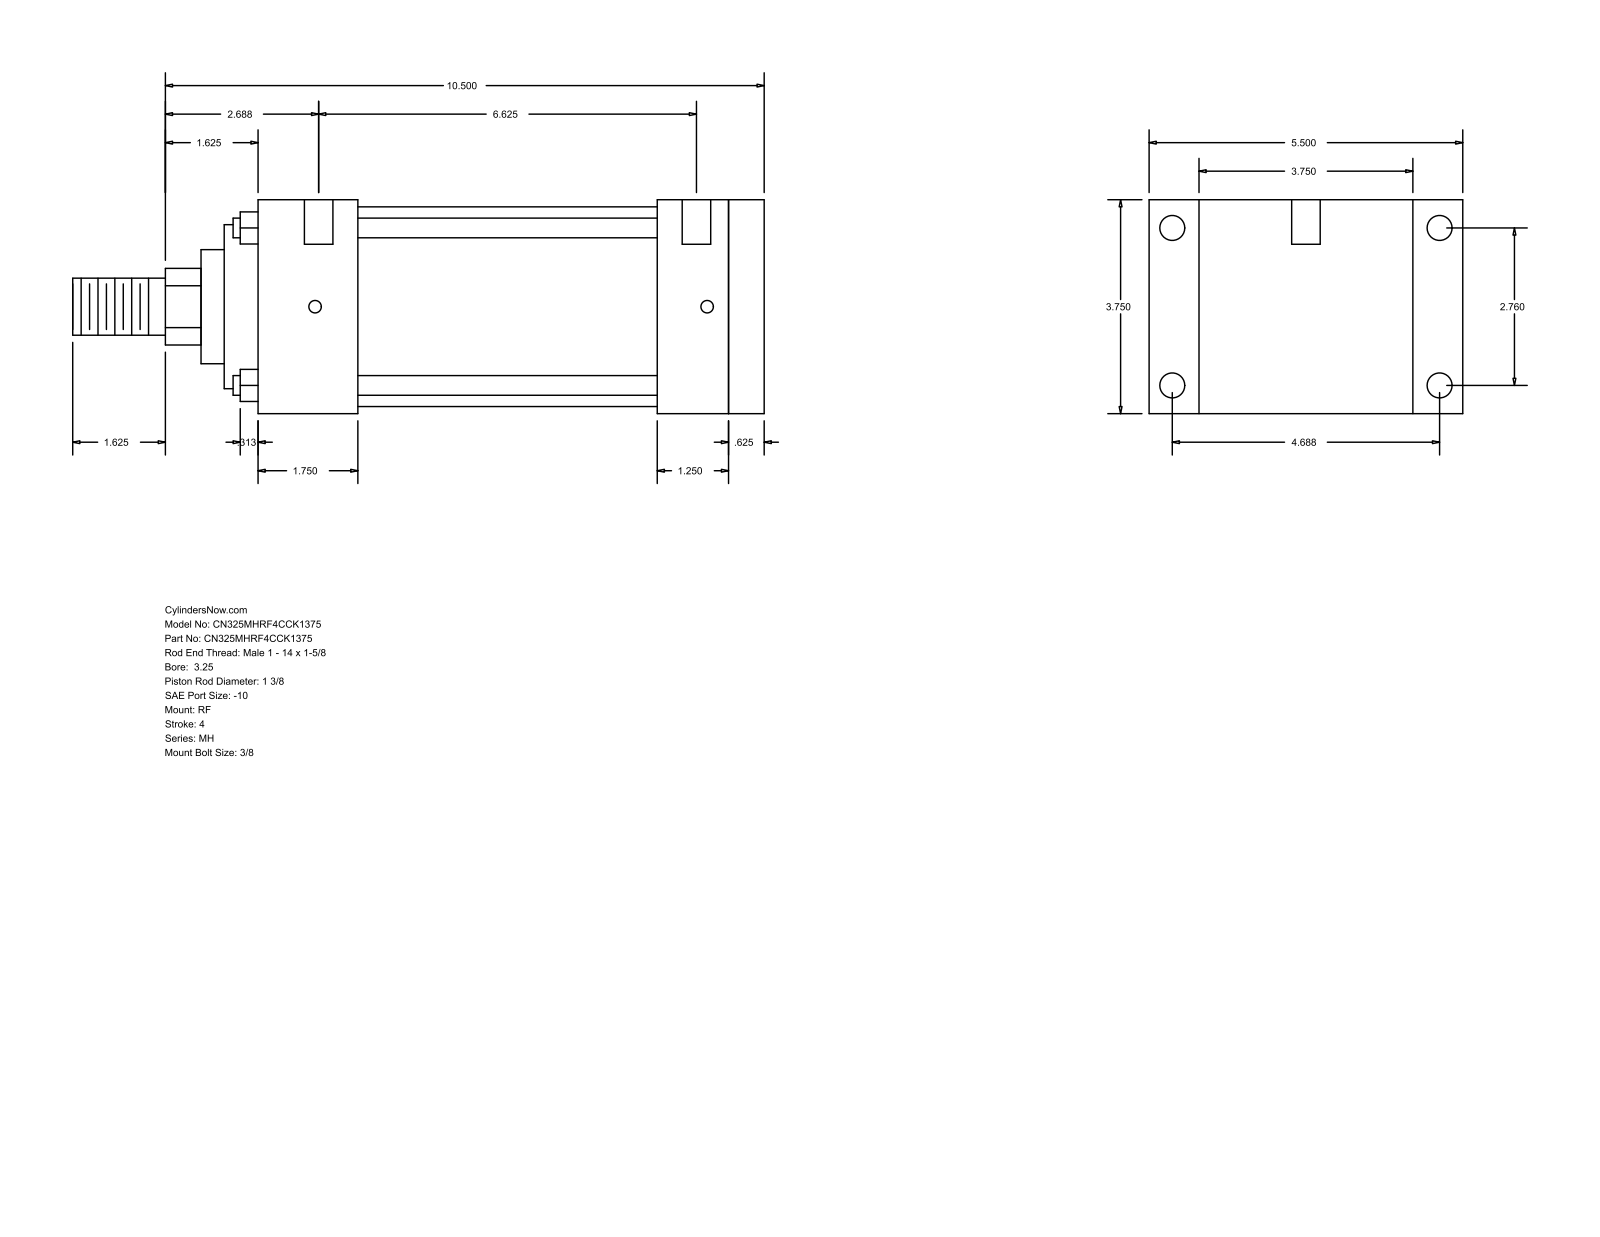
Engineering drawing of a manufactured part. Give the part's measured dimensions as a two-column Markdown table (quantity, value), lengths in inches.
| quantity | value |
| --- | --- |
| part name | MH_RF__0325_1.375 |
| STEP written by | GSSL Pune (CONFIG_CONTROL_DESIGN) |
| units | inches |
| bodies | 0 solids, 94 faces (65 planar, 29 cylindrical, 0 other) |
| overall size | 12.125 × 5.5 × 3.75 |
| round holes (diameter × count) | 0.219 × 4, 0.438 × 4, 0.5 × 2 |
| round bosses / shafts (diameter × count) | 0.345 × 4, 3.5 × 1, 2.875 × 1, 2 × 1, 1.375 × 1, 1 × 1 |
| partial cylindrical surfaces (radius × count) | 0.672 × 1 |
| main face-to-face distances | 3.75, 8.875, 0.625, 8.25, 0.875, 4.625, 1.75, 6.5, 7.125, 7 |
| hole center spacings | 2.76, 4.687, 5.439, 6.875, 0.063, 0.187, 6.625, 6.688 |
